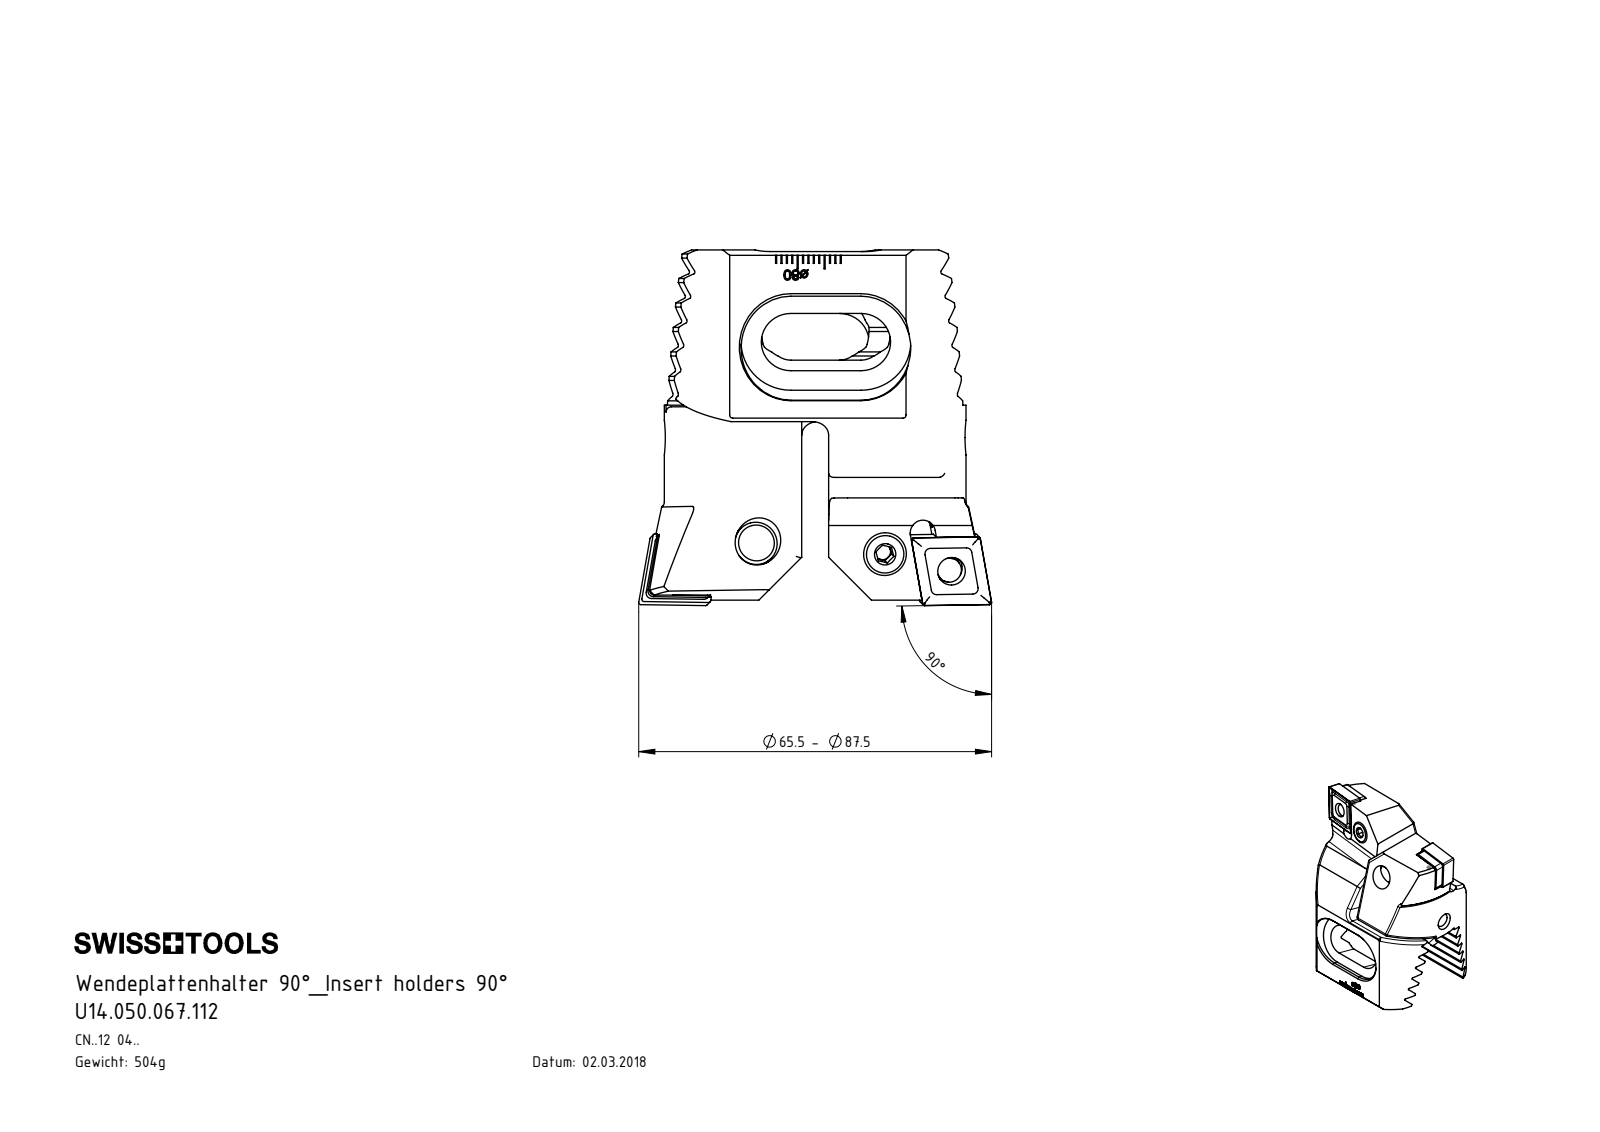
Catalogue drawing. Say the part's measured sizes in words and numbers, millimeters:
The part is named "Z55-xxx.001.037_C_CN12; CNMG120404; WCD; WCD-ER1.101.000 (+5 more)". Its 3-D file was written by "SolidWorks 2017 (AUTOMOTIVE_DESIGN)". It is 14 solids with 774 faces: 424 planar, 126 cylindrical and 224 other. Overall it measures 65.98 by 65.5 by 44.2 millimeters. Its volume is 63 389 cubic millimeters and its surface area 26 305 square millimeters. Round holes: 2 of diameter 2, 2 of diameter 5.16, 2 of diameter 6.4, 2 of diameter 7, 2 of diameter 8.4, 1 of diameter 5. Round bosses or shafts: 2 of diameter 8, 2 of diameter 7.9, 2 of diameter 6.4, 2 of diameter 4.5, 2 of diameter 3.55, 1 of diameter 6, 1 of diameter 4. Partial cylindrical surfaces (rounded edges, fillets, slot ends): 22 of radius 1, 12 of radius 0.34, 8 of radius 0.4, 6 of radius 2.5, 6 of radius 3, 4 of radius 5.5, 4 of radius 9.25, 4 of radius 12. The main face-to-face distances are 4.07, 8.14, 12.21, 16.28, 20.35, 7.85, 1.69, 5, 0.5, 44.2. The hole center spacings are 12.81, 12.86, 16, 30.9.
